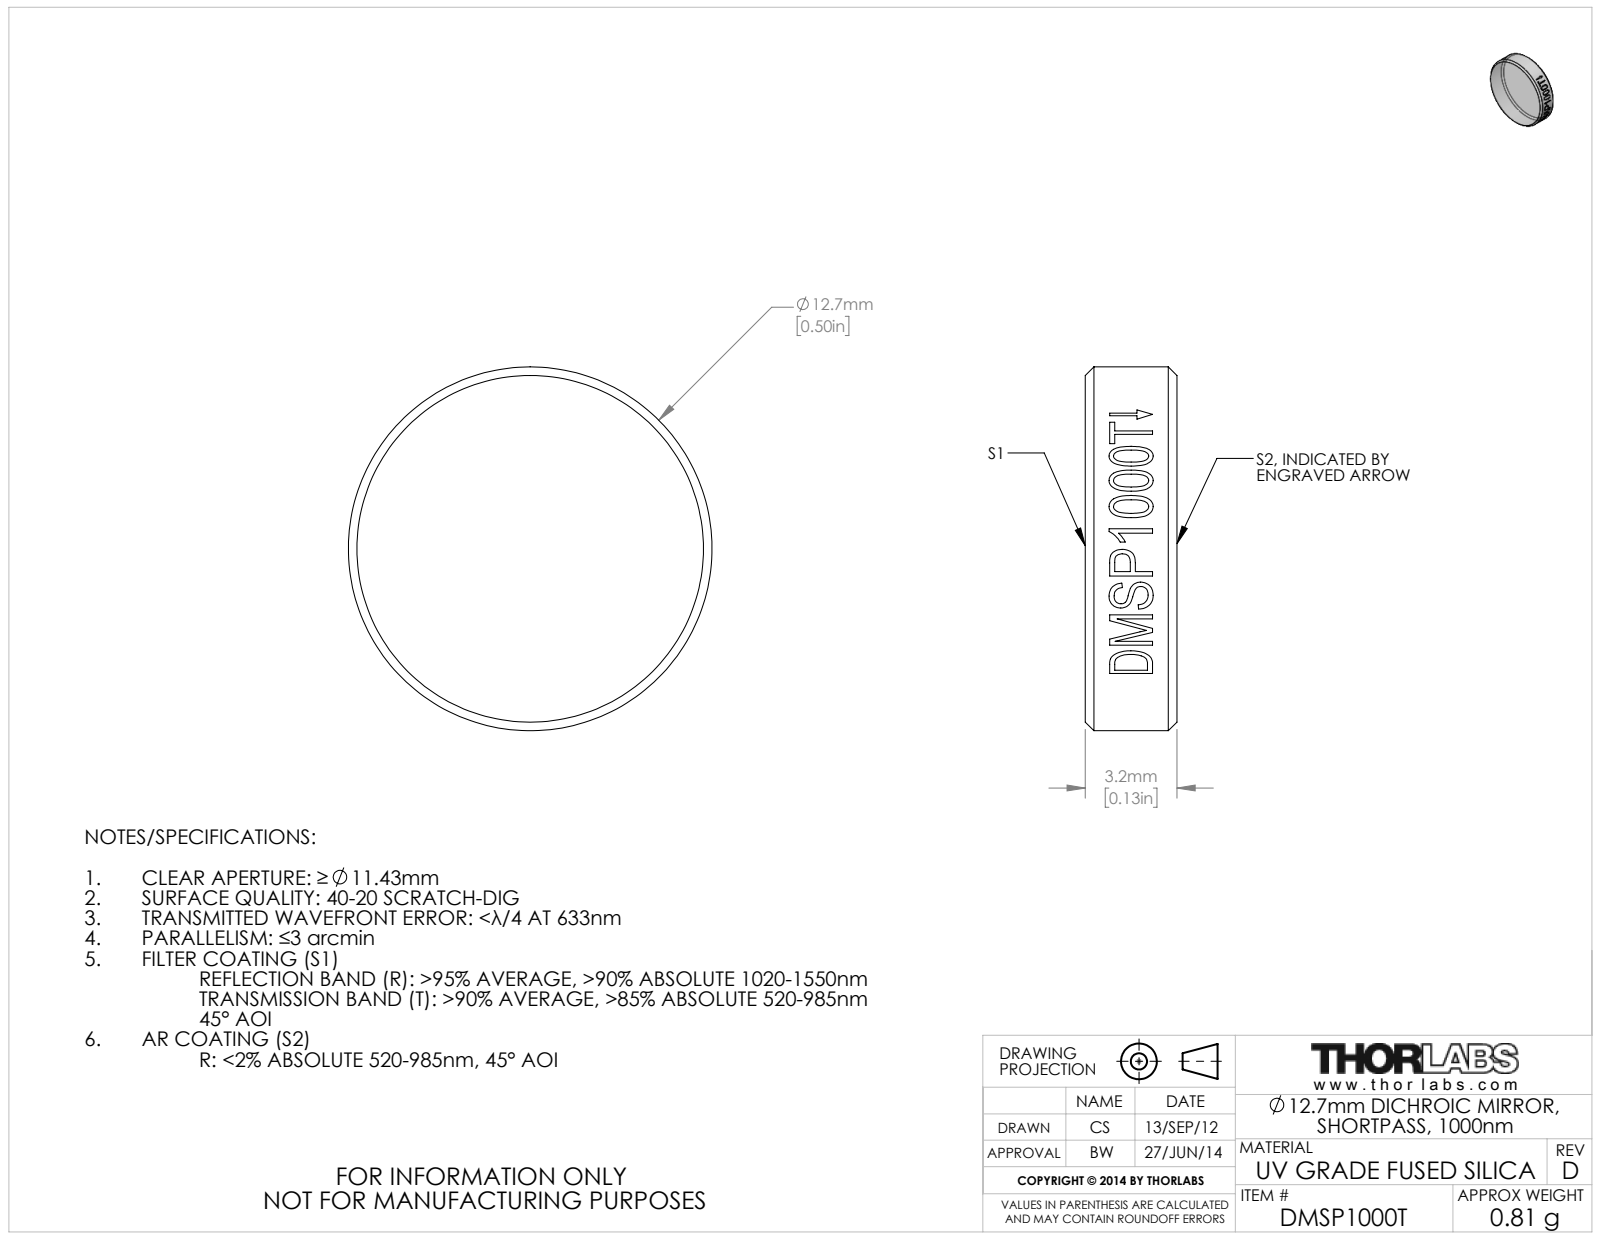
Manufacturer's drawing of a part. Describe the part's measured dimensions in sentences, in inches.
The part is named "24968-E0W". Its 3-D file was written by "SolidWorks 2011 (CONFIG_CONTROL_DESIGN)". It is 0 solids with 23 faces: 2 planar, 17 cylindrical and 4 other. Overall it measures 0.5 by 0.5 by 0.126 inches. Round bosses or shafts: 1 of diameter 0.5. The main face-to-face distances are 0.126.
